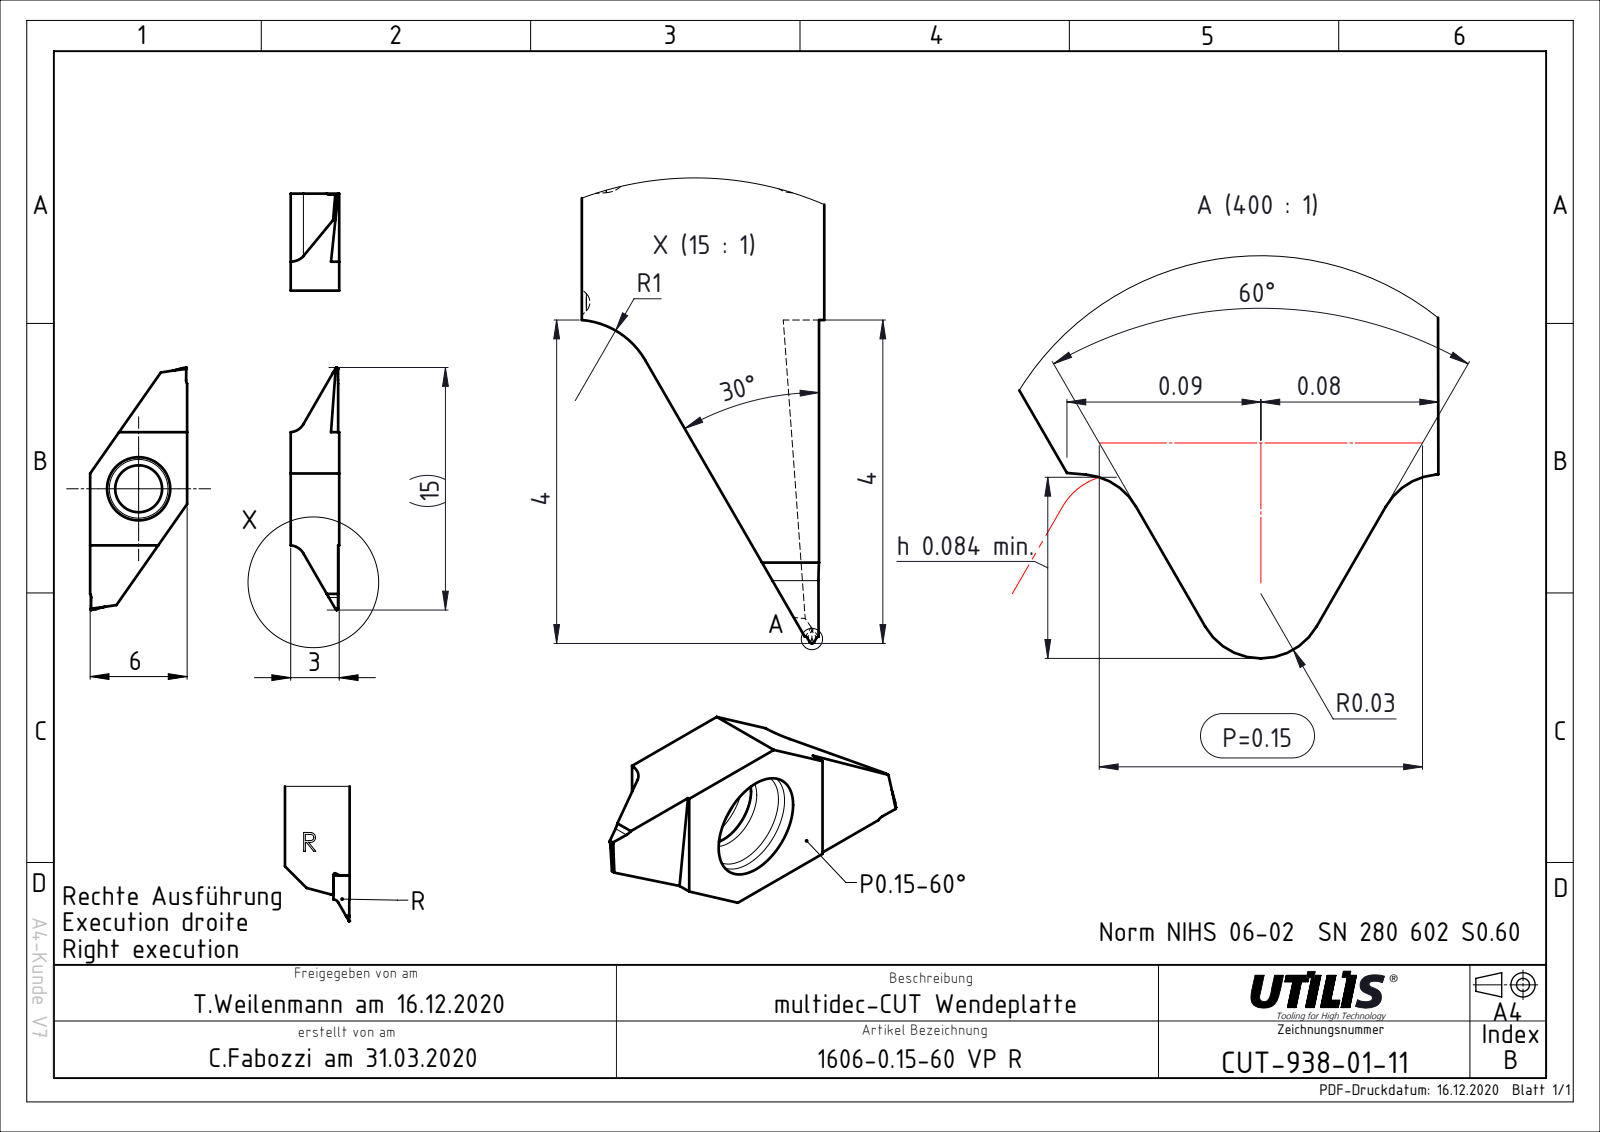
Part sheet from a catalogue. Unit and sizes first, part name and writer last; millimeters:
Units: millimetres
Overall size (bounding box): 15 × 6 × 3
Round holes (diameter × count): ⌀2.9 ×1
Partial cylindrical surfaces — rounded edges, fillets, slot ends (radius × count): R1 ×2
Main face-to-face distances: 6, 3, 9, 7, 12, 7.21, 7.2, 14.45, 14.46
Volume: 125 mm³ · Surface area: 209 mm²
Bodies: 1 solid, 36 faces (22 planar, 14 cylindrical, 0 other)
Part name (STEP PRODUCT): CUT-938-01; ASME Y14.5
STEP written by: FormatWorks Professional (AP242_MANAGED_MODEL_BASED_3D_ENGINEERING_MIM_LF)
